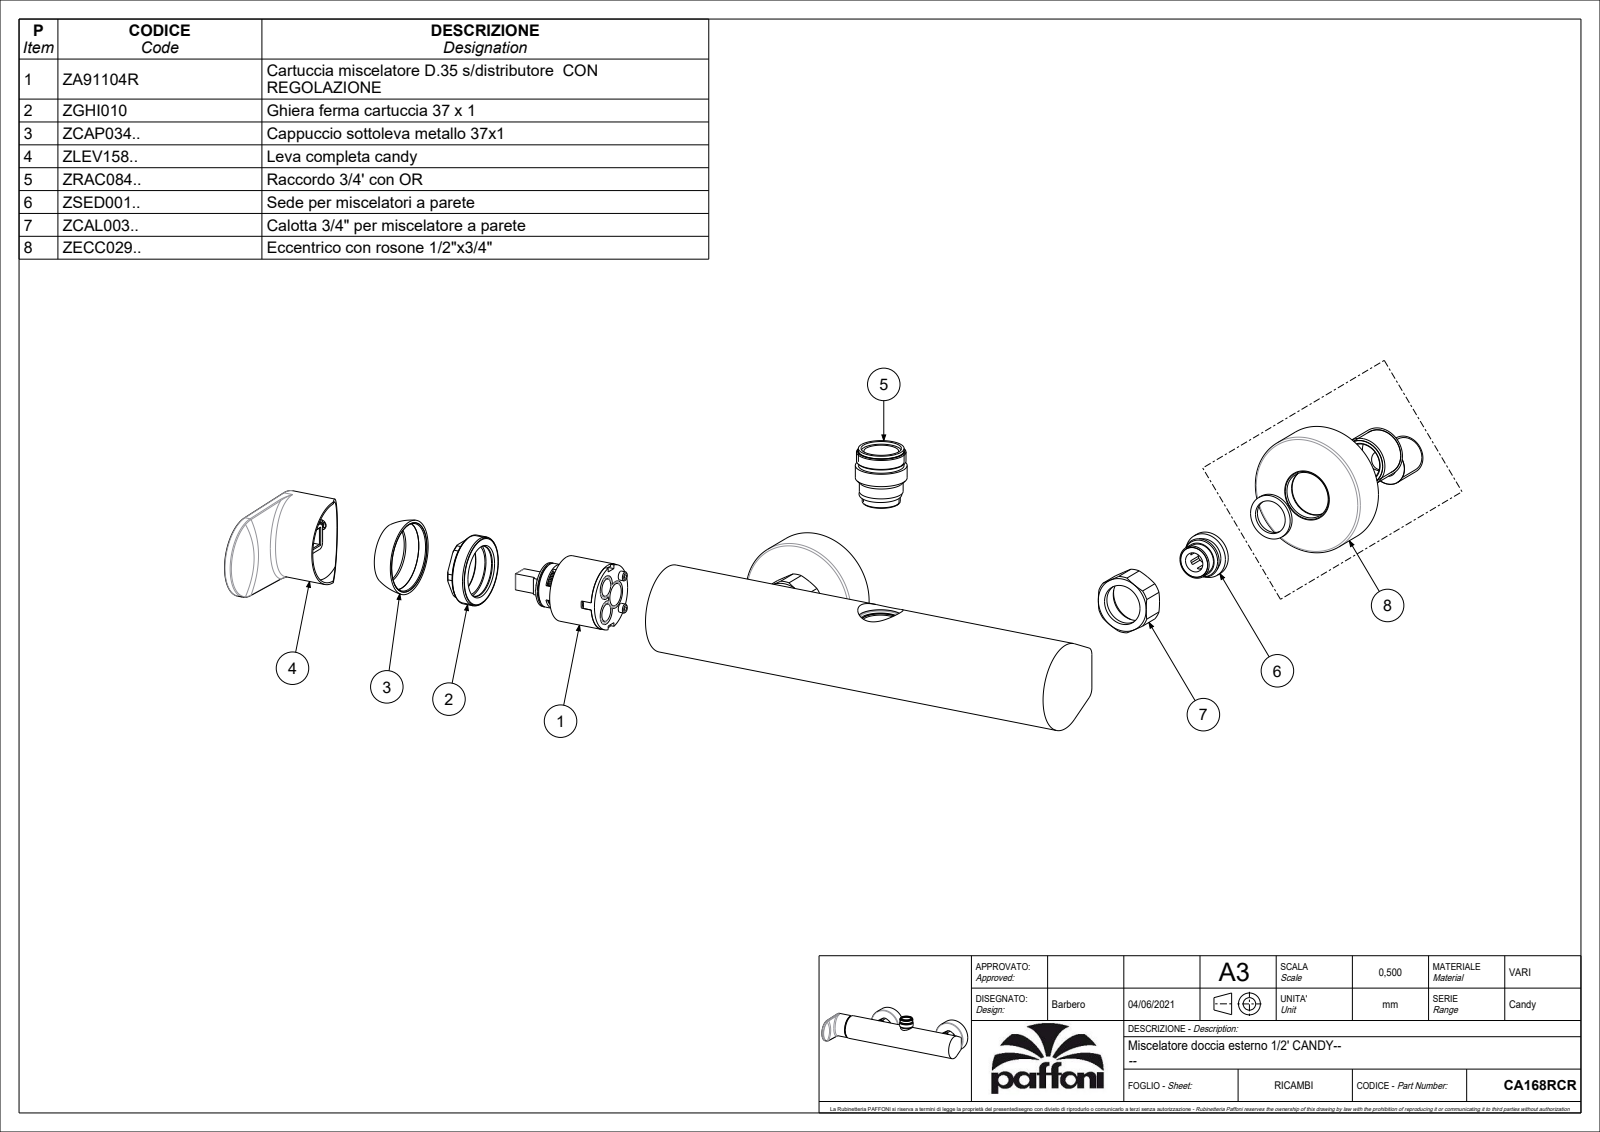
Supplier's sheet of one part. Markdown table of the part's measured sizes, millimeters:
| quantity | value |
| --- | --- |
| part name | CA168RCR |
| STEP written by | CREO PARAMETRIC BY PTC INC, 2020044 (CONFIG_CONTROL_DESIGN) |
| units | millimeters |
| bodies | 2 solids, 519 faces (165 planar, 173 cylindrical, 181 other) |
| overall size | 273.6 × 125.5 × 74.2 |
| volume | 353 004 mm³ |
| surface area | 130 333 mm² |
| round holes (diameter × count) | 10.5 × 3, 3 × 1, 3.5 × 1, 4.5 × 1, 12.5 × 1, 15.1 × 1, 16 × 1, 18.2 × 1, 19 × 1, 20 × 1, 21.2 × 1, 23.8 × 1 |
| round bosses / shafts (diameter × count) | 63.5 × 2, 17.7 × 2, 45 × 1, 27.2 × 1, 26 × 1, 24 × 1, 23 × 1, 7.6 × 1 |
| partial cylindrical surfaces (radius × count) | 1.5 × 44, 3 × 4, 1.3 × 2, 5 × 2, 15.5 × 2, 18.5 × 2, 3.5 × 1, 14 × 1 |
| main face-to-face distances | 3.7, 20, 49.2, 29.2, 35, 15, 3.5, 45.7, 25.7, 10.7 |
| hole center spacings | 6, 73.6, 150, 223.6 |
